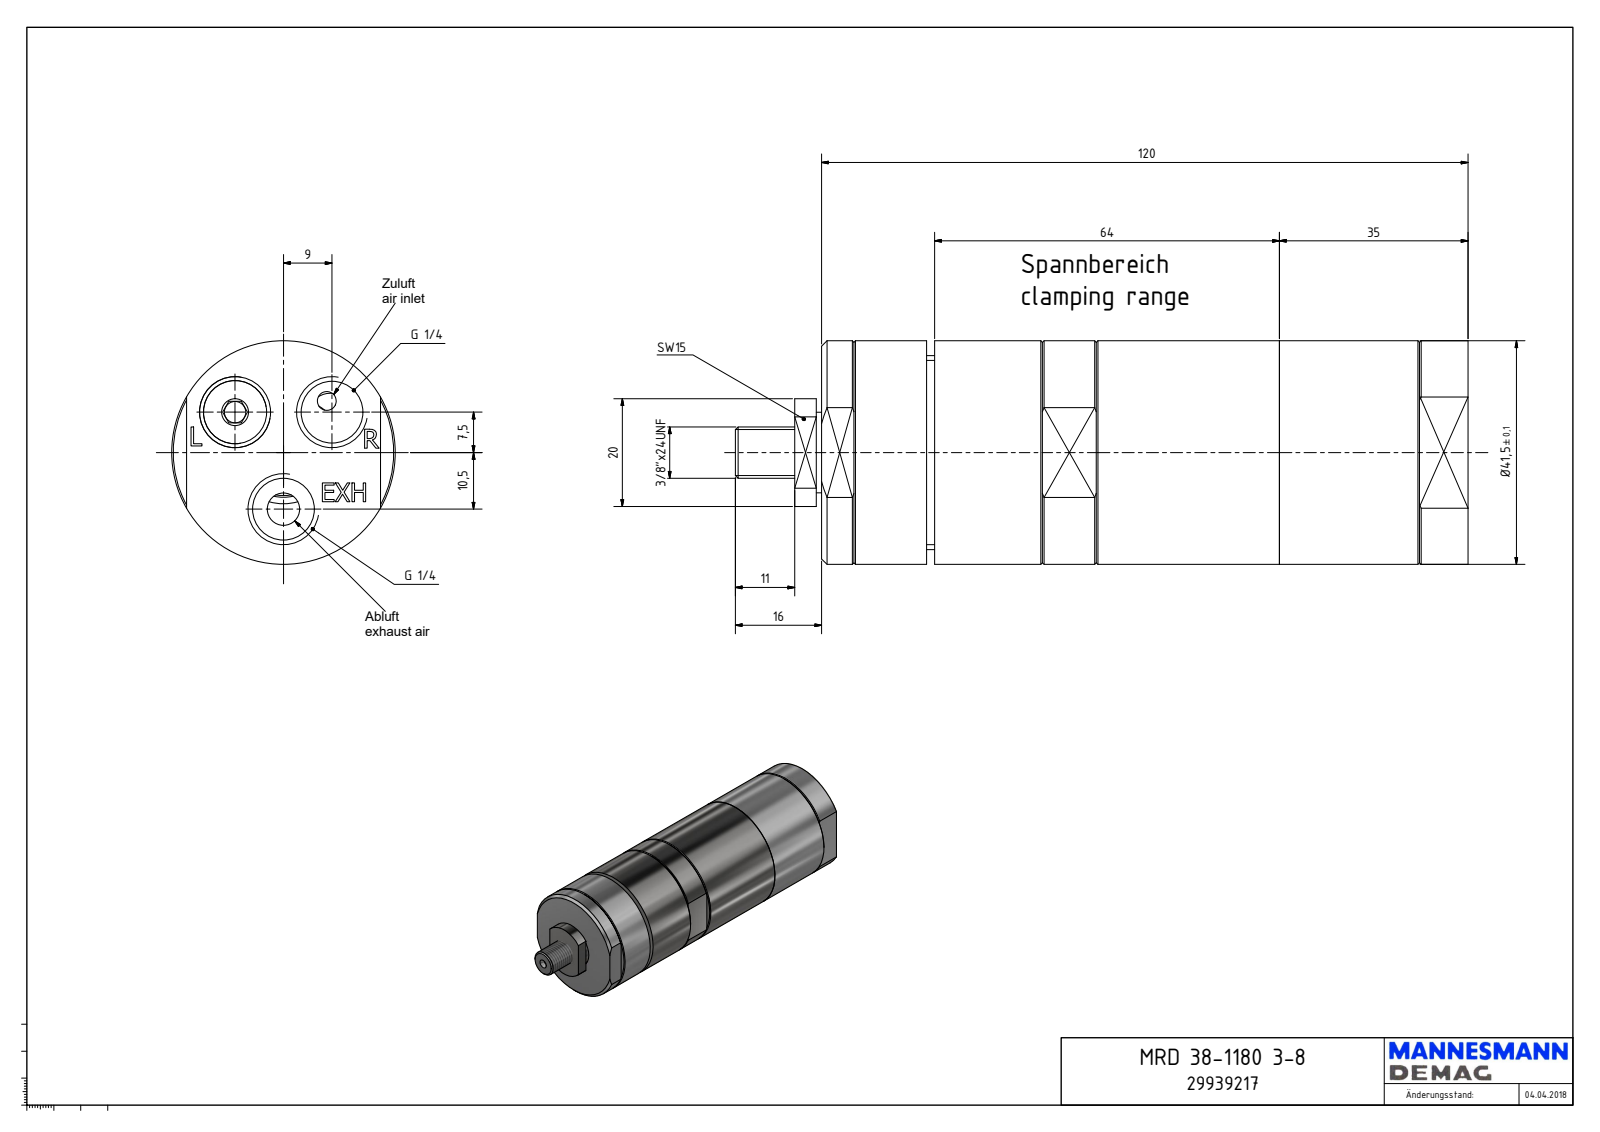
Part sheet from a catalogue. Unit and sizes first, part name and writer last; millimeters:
Units: millimetres
Overall size (bounding box): 136 × 41.5 × 41.5
Round holes (diameter × count): ⌀11.45 ×3, ⌀1.6 ×1, ⌀4 ×1, ⌀16 ×1
Round bosses / shafts (diameter × count): ⌀41.5 ×1, ⌀36 ×1, ⌀14.95 ×1, ⌀9.53 ×1
Partial cylindrical surfaces — rounded edges, fillets, slot ends (radius × count): R10 ×1
Main face-to-face distances: 120, 1, 37, 19.5, 21, 1.5, 100.5, 99, 109.44, 89.94
Hole centre spacings: 11.72, 20.12, 10.5, 18
Volume: 160 050 mm³ · Surface area: 20 962 mm²
Bodies: 1 solid, 151 faces (100 planar, 21 cylindrical, 30 other)
Part name (STEP PRODUCT): MRD 38-1180 3-8_29939217
STEP written by: Autodesk Inventor 2018 (AUTOMOTIVE_DESIGN)
